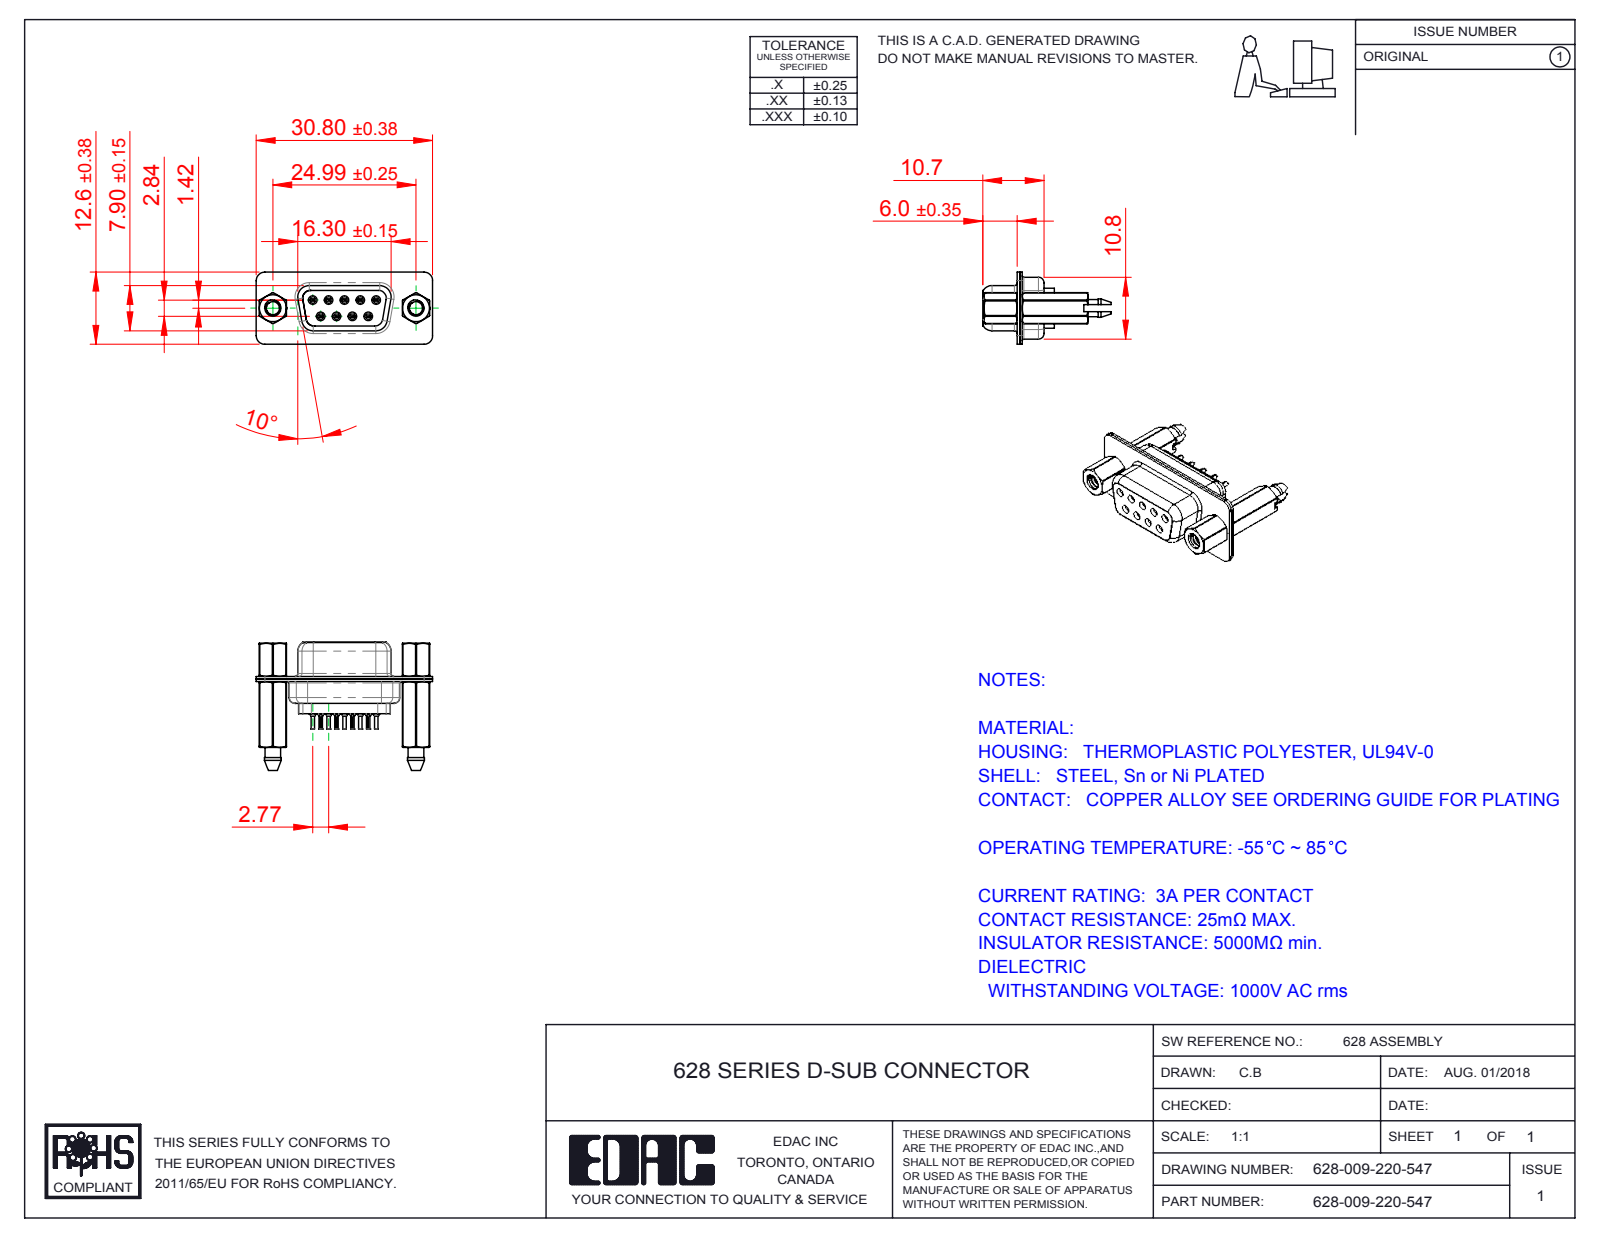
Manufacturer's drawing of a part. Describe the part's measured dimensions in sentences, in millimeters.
The part is named "628 Housing_09 LP; 628 Contact Row 1_20L; 628 4-40 Hex Standoff; 628 Contact Row 2_20L (+4 more)". Its 3-D file was written by "SolidWorks 2016 (CONFIG_CONTROL_DESIGN)". It is 16 solids with 1656 faces: 400 planar, 572 cylindrical and 684 other. Overall it measures 30.8 by 22.4 by 12.6 millimeters. Its volume is 2 240 cubic millimeters and its surface area 5 553 square millimeters. Round holes: 9 of diameter 0.2, 9 of diameter 0.8, 9 of diameter 0.9, 9 of diameter 1.1, 9 of diameter 1.6, 5 of diameter 1.7, 2 of diameter 2.26, 2 of diameter 2.29, 2 of diameter 4, 2 of diameter 4.8. Round bosses or shafts: 9 of diameter 2, 9 of diameter 1.5, 9 of diameter 1.2, 9 of diameter 0.6, 2 of diameter 4.9, 2 of diameter 2.79. Partial cylindrical surfaces (rounded edges, fillets, slot ends): 18 of radius 0.1, 18 of radius 1.5, 12 of radius 2, 9 of radius 0.28, 7 of radius 1.35, 6 of radius 1.6, 4 of radius 0.25, 4 of radius 0.5. The main face-to-face distances are 0.45, 0.4, 0.9, 4.76, 12.5, 1.9, 8.5, 6.6, 1.4, 0.5. The hole center spacings are 3.16, 2.77, 5.54, 5.03, 5.04, 8.31, 7.48, 7.49.
